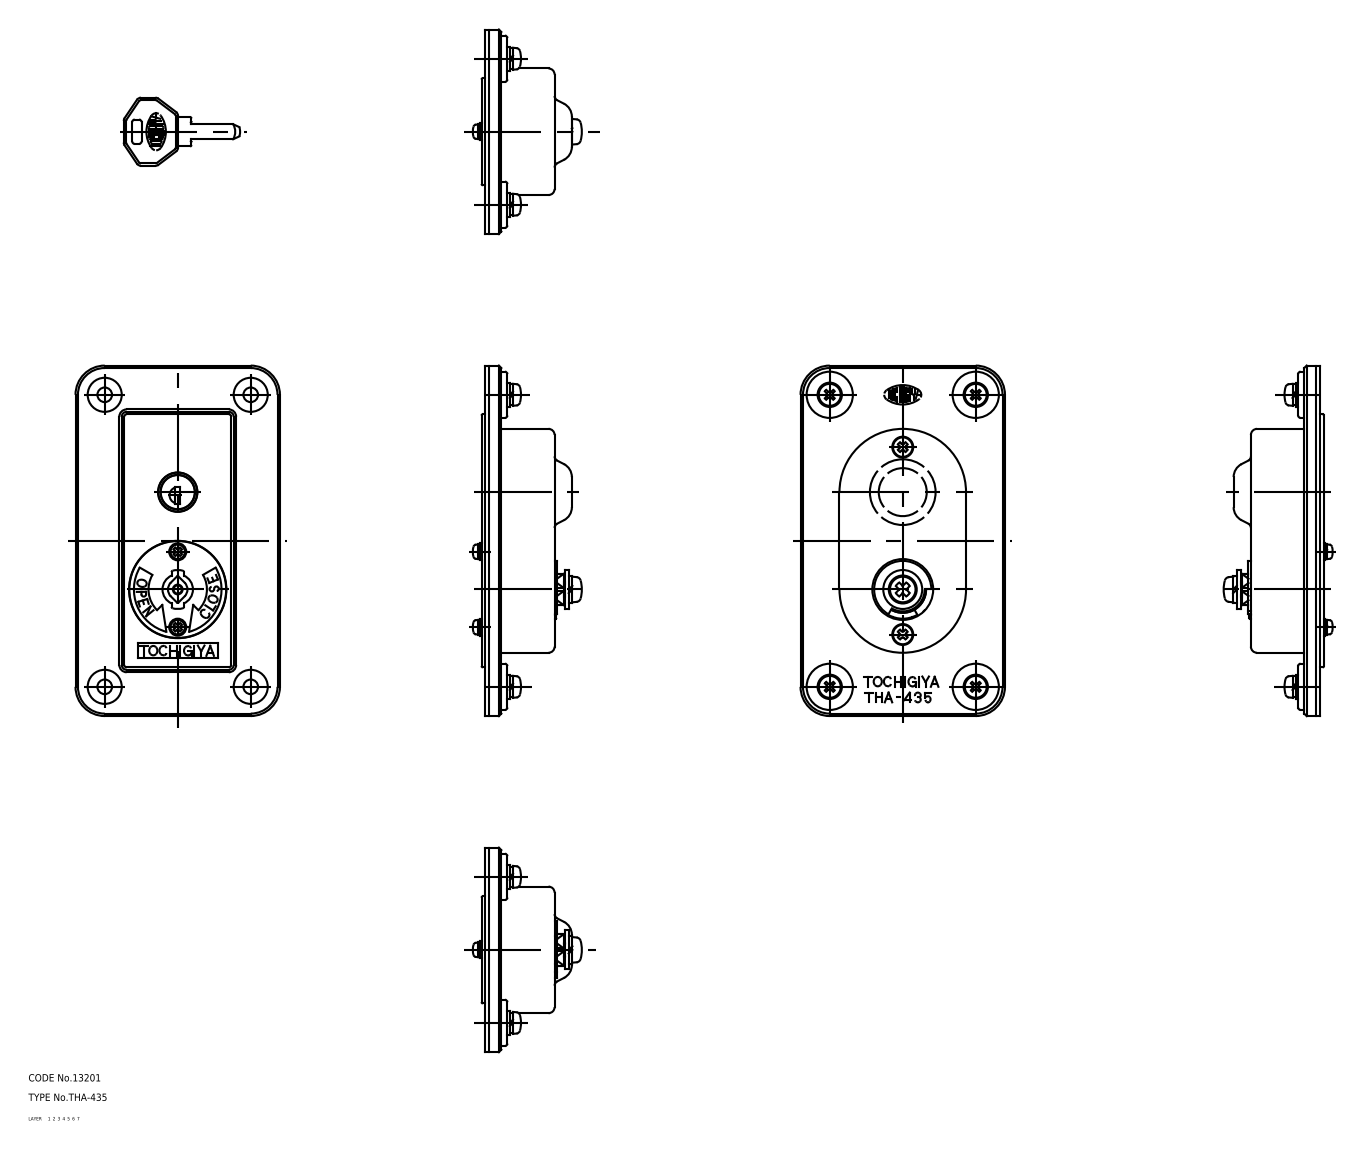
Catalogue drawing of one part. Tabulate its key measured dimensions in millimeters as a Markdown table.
| quantity | value |
| --- | --- |
| part name | screw_C; screw; screw_B; washer (+8 more) |
| STEP written by | CADfix (AUTOMOTIVE_DESIGN) |
| units | millimeters |
| bodies | 18 solids, 738 faces (0 planar, 0 cylindrical, 738 other) |
| overall size | 144 × 135.02 × 84 |
| volume | 110 732 mm³ |
| surface area | 80 454 mm² |
